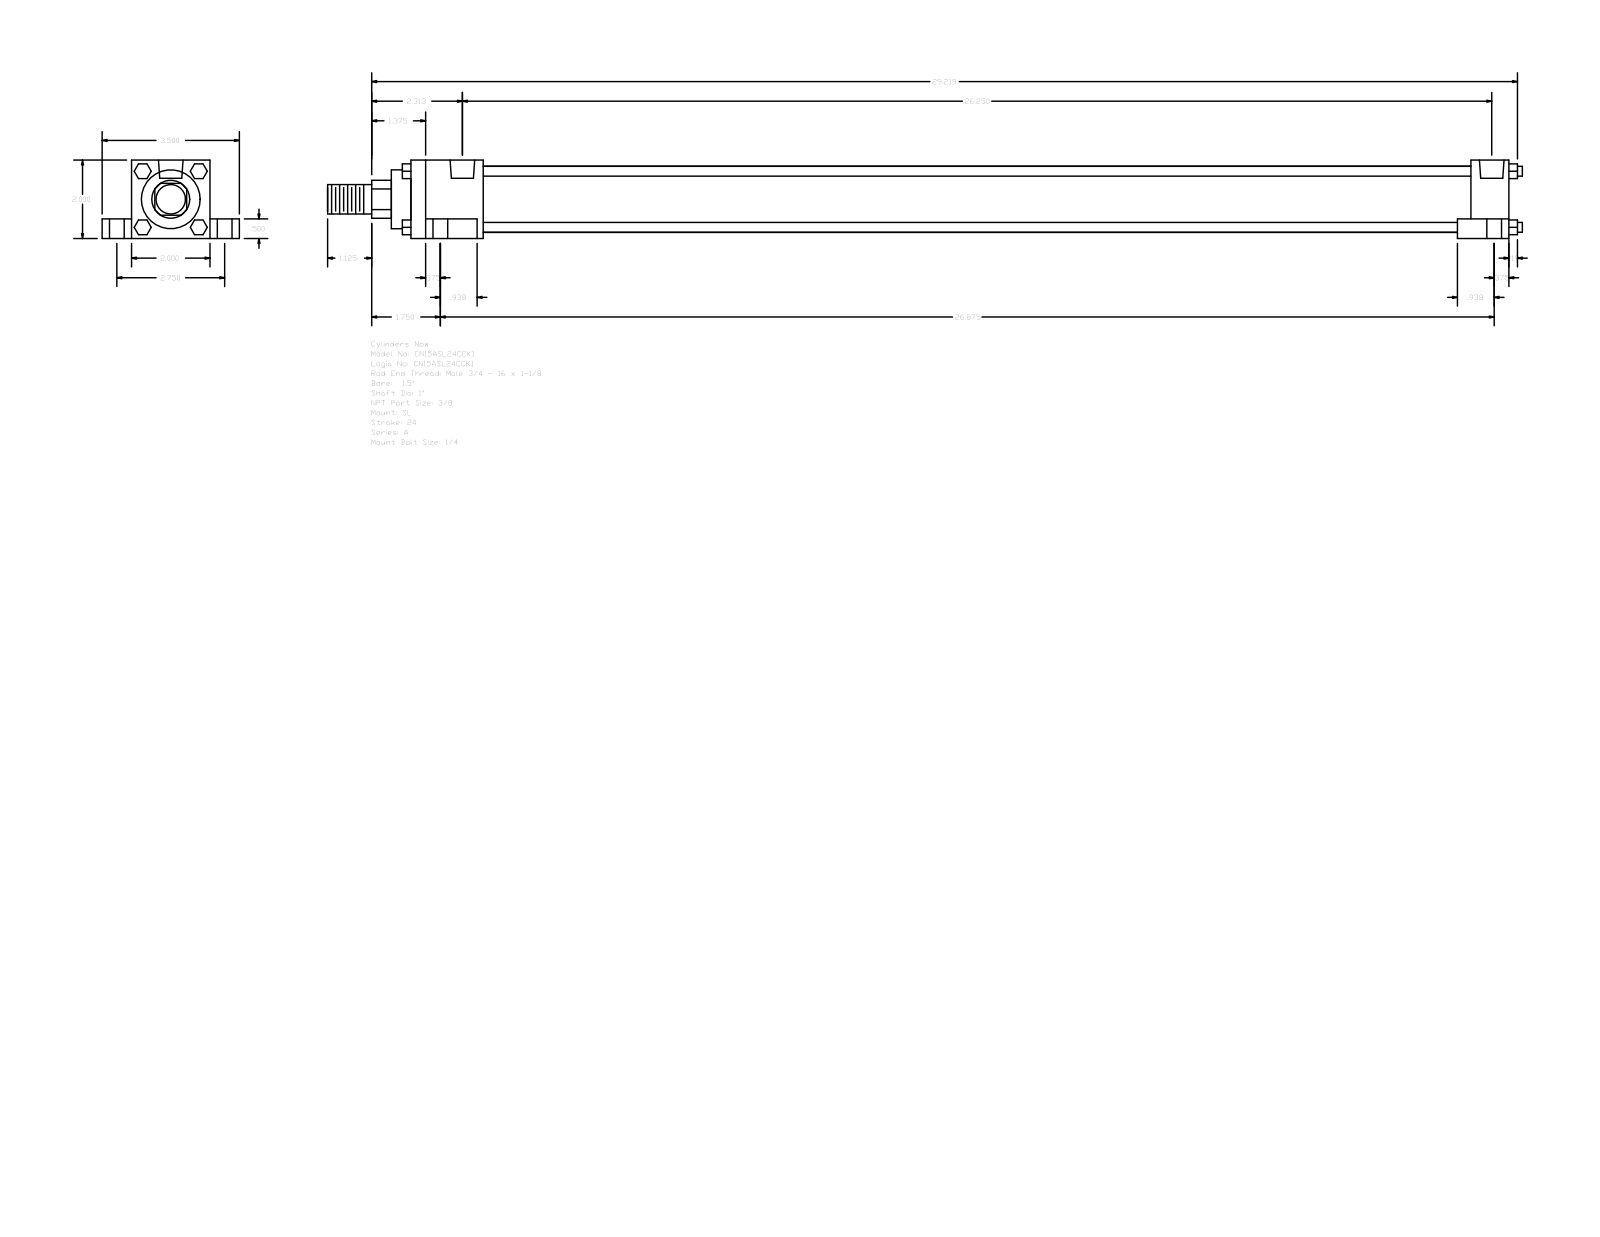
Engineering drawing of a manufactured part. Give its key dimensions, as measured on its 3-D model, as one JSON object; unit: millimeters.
{"part_name": "A_SL__0150_1", "step_written_by": "GSSL Pune (CONFIG_CONTROL_DESIGN)", "units": "millimeters", "bodies": {"solids": 0, "faces": 148, "planar": 112, "cylindrical": 36, "other": 0}, "overall_size": [773.91, 88.9, 50.8], "round_holes": [[5.56, 4], [9.53, 4], [15.88, 4], [15.93, 2]], "round_bosses_or_shafts": [[6.35, 4], [42.93, 1], [38.1, 1], [25.4, 1], [19.05, 1]], "partial_cylinders_radius": [[12.29, 1]], "face_to_face_distances": [50.8, 12.7, 38.1, 19.05, 69.85, 9.52, 711.2, 33.34, 686.59, 24.61], "hole_center_spacings": [3.97, 34.96, 35.36, 37.73, 39.41, 69.84, 658.81, 662.78]}
